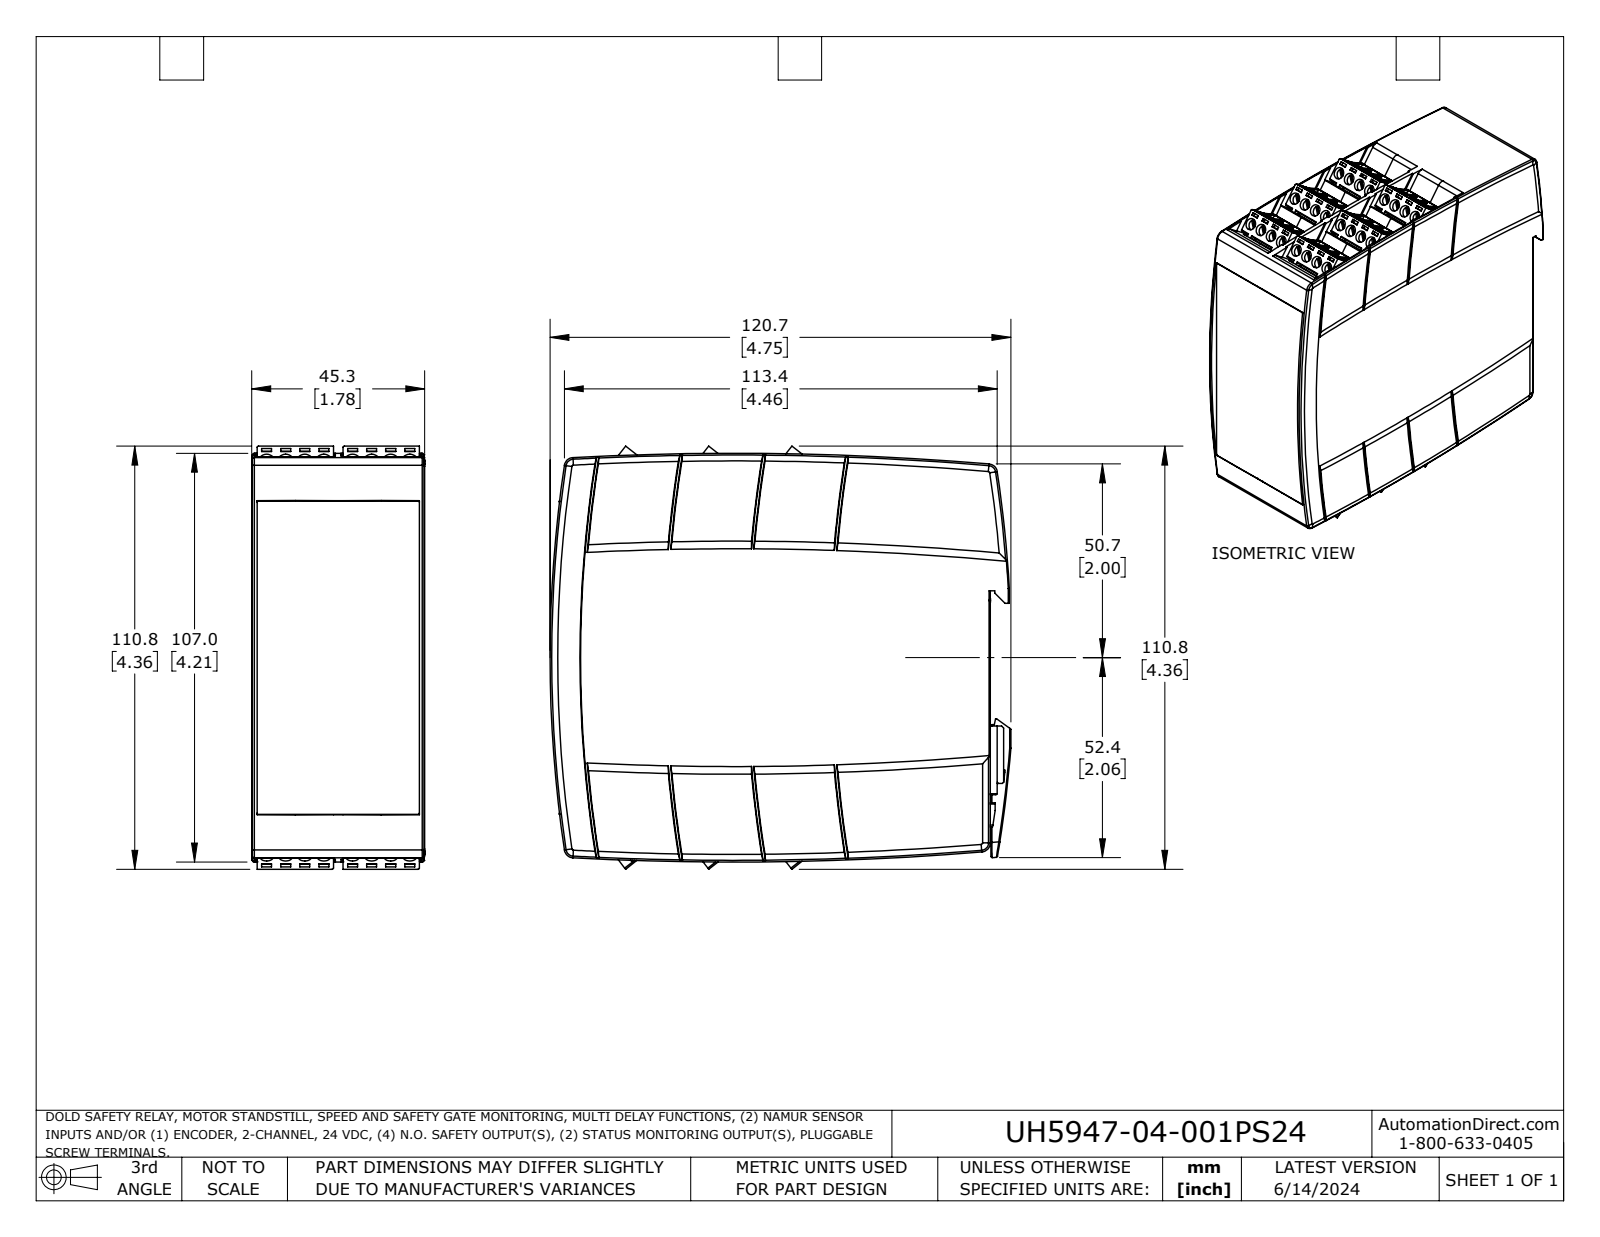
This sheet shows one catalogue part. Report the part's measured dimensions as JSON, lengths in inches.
{"part_name": "PS_UH5947", "step_written_by": "SolidWorks 2023 (AUTOMOTIVE_DESIGN)", "units": "inches", "bodies": {"solids": 1, "faces": 2796, "planar": 2430, "cylindrical": 227, "other": 139}, "overall_size": [4.752, 4.362, 1.783], "volume_in3": 32, "surface_area_in2": 110.6, "round_holes": [[0.157, 48]], "round_bosses_or_shafts": [[0.149, 48]], "partial_cylinders_radius": [[0.016, 19], [0.012, 12], [0.094, 8], [0.02, 7], [0.014, 4], [12.795, 2], [31.417, 2], [31.496, 2]], "face_to_face_distances": [1.776, 1.768, 1.783, 0.886, 0.675, 0.02, 0.807, 0.528, 0.079, 4.443], "hole_center_spacings": [0.197, 1.031, 0.394, 0.563, 0.563, 0.886, 1.074, 1.204]}
